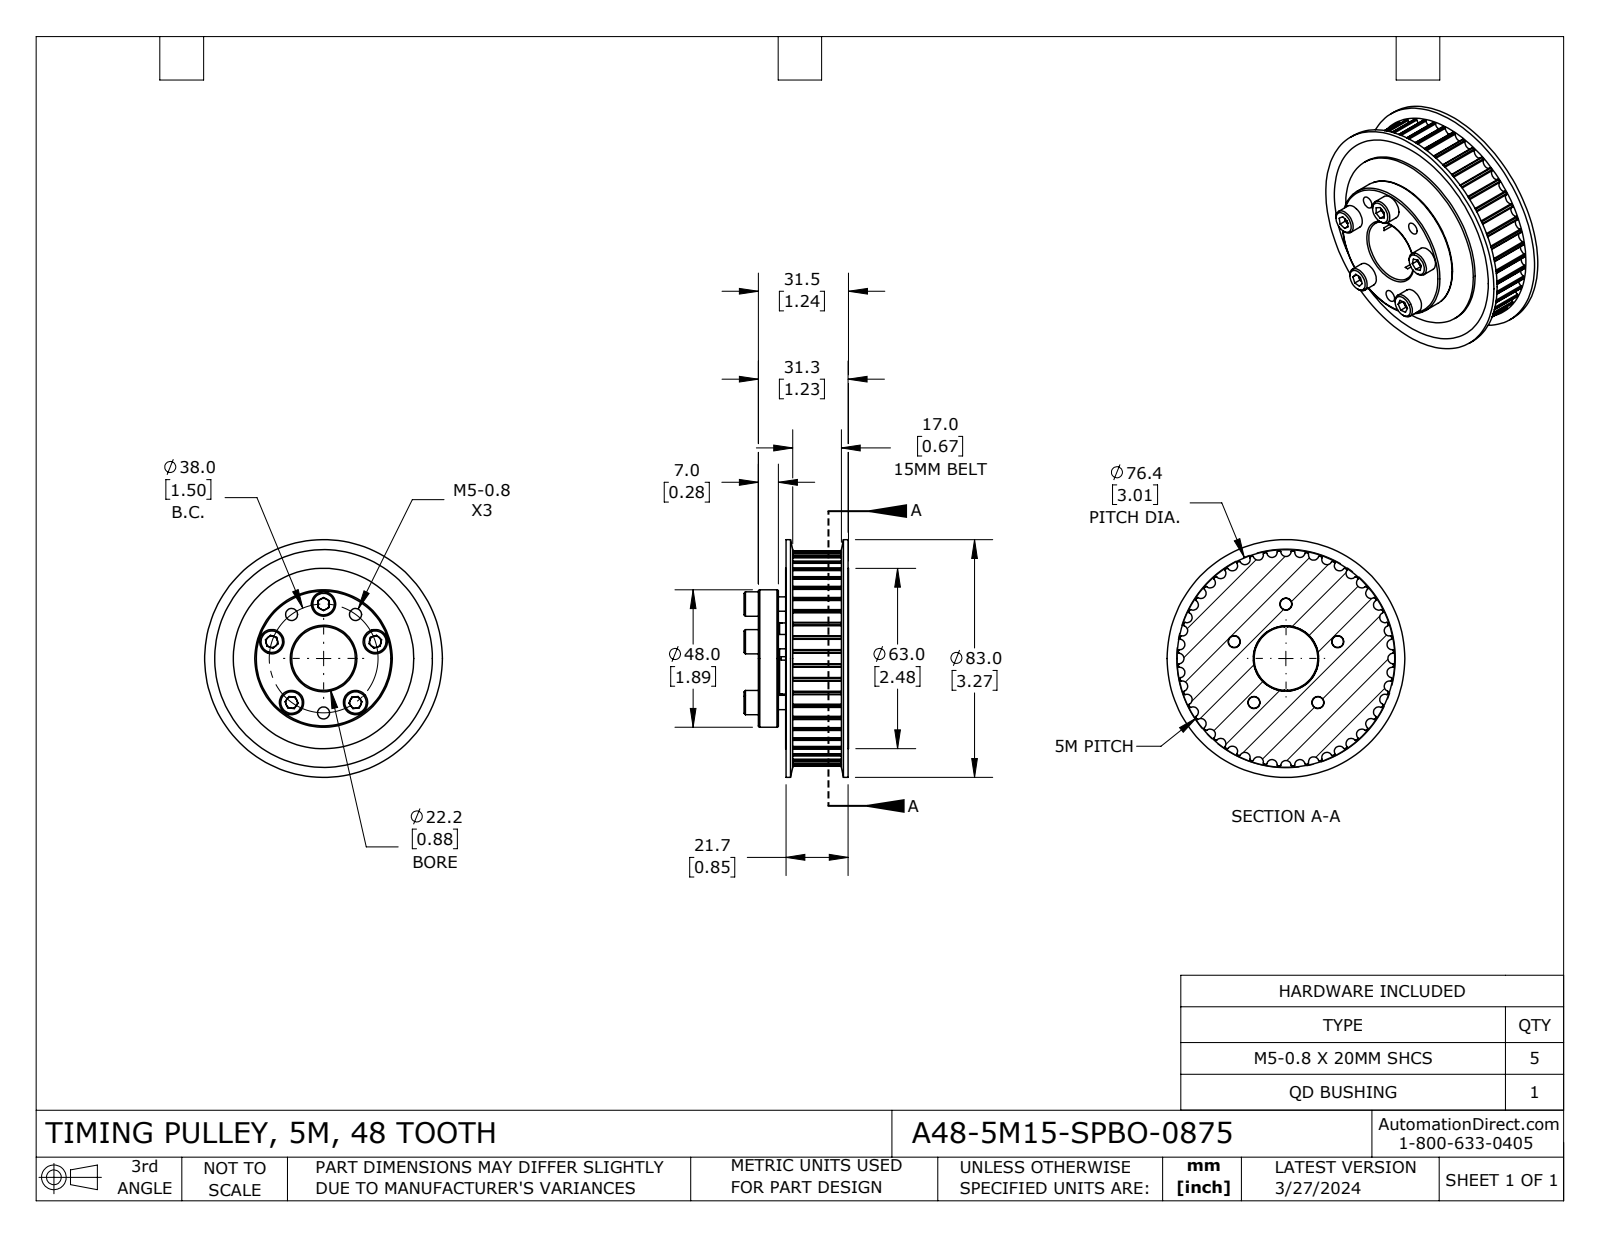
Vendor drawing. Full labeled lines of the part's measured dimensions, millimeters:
Part name (STEP PRODUCT): A48-5M15-SPBO-0875
STEP written by: SolidWorks 2021 (CONFIG_CONTROL_DESIGN)
Units: millimetres
Bodies: 9 solids, 474 faces (101 planar, 307 cylindrical, 66 other)
Overall size (bounding box): 83 × 83 × 36.5
Volume: 96 056 mm³ · Surface area: 37 672 mm²
Round holes (diameter × count): ⌀4.2 ×8, ⌀5.5 ×5, ⌀22.22 ×1, ⌀24.83 ×1, ⌀63 ×1
Round bosses / shafts (diameter × count): ⌀8.5 ×5, ⌀5 ×5, ⌀83 ×1, ⌀48 ×1, ⌀24.82 ×1
Partial cylindrical surfaces — rounded edges, fillets, slot ends (radius × count): R0.3 ×96, R1.82 ×48, R37.62 ×1
Main face-to-face distances: 2.5, 19.5, 22, 0.9, 21.1, 1.6, 18.6, 17, 12, 20.2
Hole centre spacings: 19, 36.14, 30.74, 11.75, 22.34, 38, 11.74, 22.33
